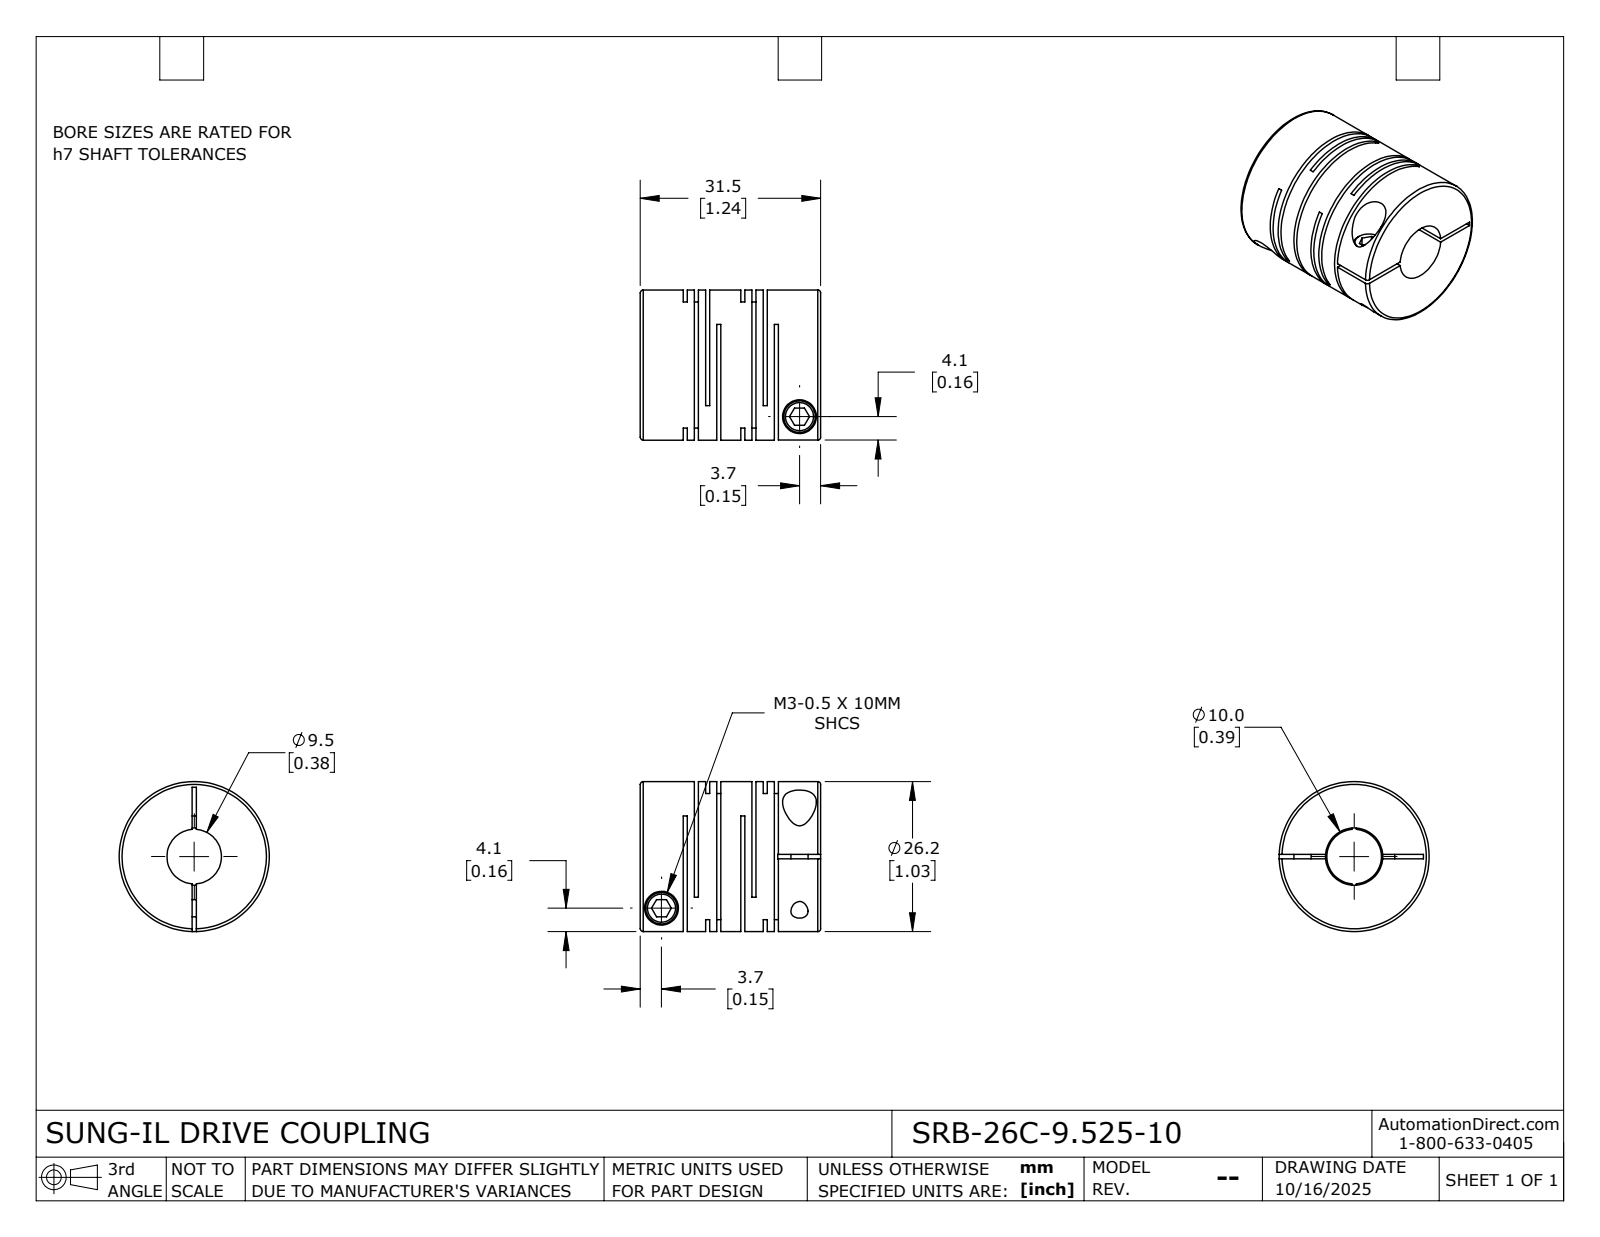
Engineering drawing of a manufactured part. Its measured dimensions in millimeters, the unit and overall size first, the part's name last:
Units: millimetres
Overall size (bounding box): 31.5 × 26.2 × 26.2
Round holes (diameter × count): ⌀3 ×2, ⌀5.9 ×2, ⌀9.53 ×1, ⌀10 ×1
Round bosses / shafts (diameter × count): ⌀5.5 ×2, ⌀26.2 ×1
Main face-to-face distances: 1.95, 10.05, 0.71, 3.9, 8.1, 12, 1.24, 2.66, 9.34, 13.95
Volume: 11 994 mm³ · Surface area: 10 733 mm²
Bodies: 1 solid, 115 faces (60 planar, 42 cylindrical, 13 other)
Part name (STEP PRODUCT): SRB-26C-9.525-10
STEP written by: SolidWorks 2024 (CONFIG_CONTROL_DESIGN)
